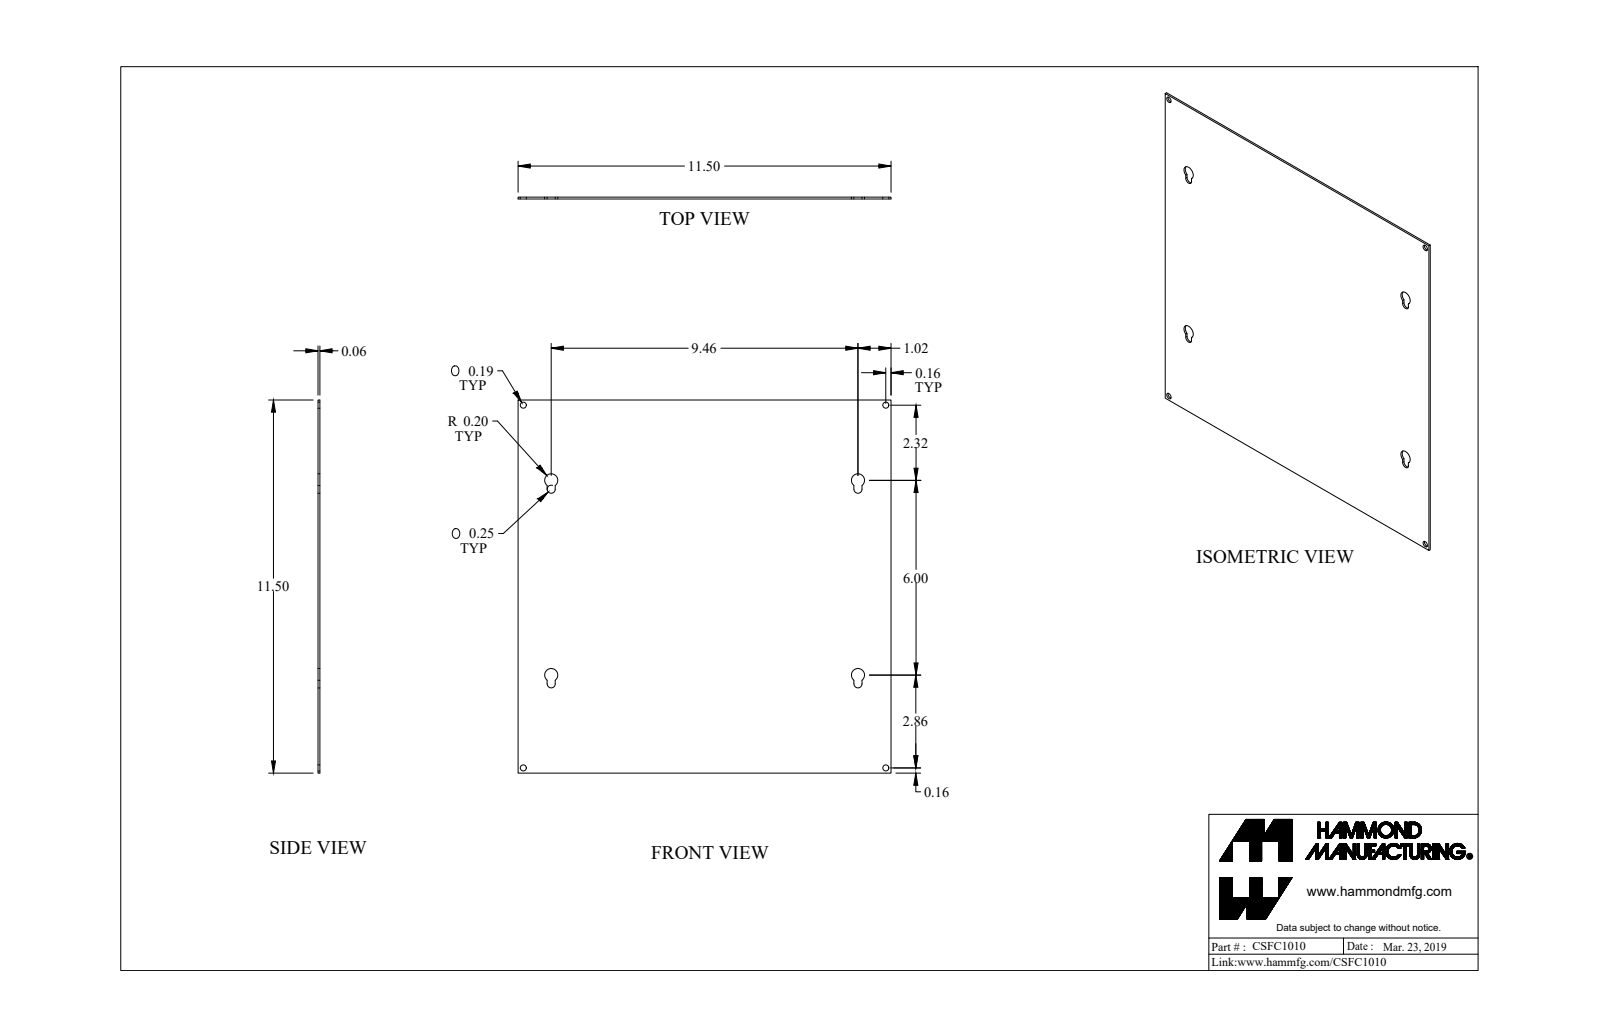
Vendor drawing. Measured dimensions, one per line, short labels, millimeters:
name: CSFC1010_Default
written by: SolidWorks 2019 (CONFIG_CONTROL_DESIGN)
unit: mm
bodies: 1 solid, 38 faces (14 planar, 24 cylindrical, 0 other)
size: 292.1 × 292.1 × 1.4
volume: 122 800 mm³; area: 171 600 mm²
holes: 4× ⌀4.8
rounds: 4× R3.2, 4× R5.2
face distances: 1.4, 292.1, 22.7, 269.4, 29.1, 263, 240.3, 6.4, 246.6, 233.9
hole spacings: 284, 401.6
